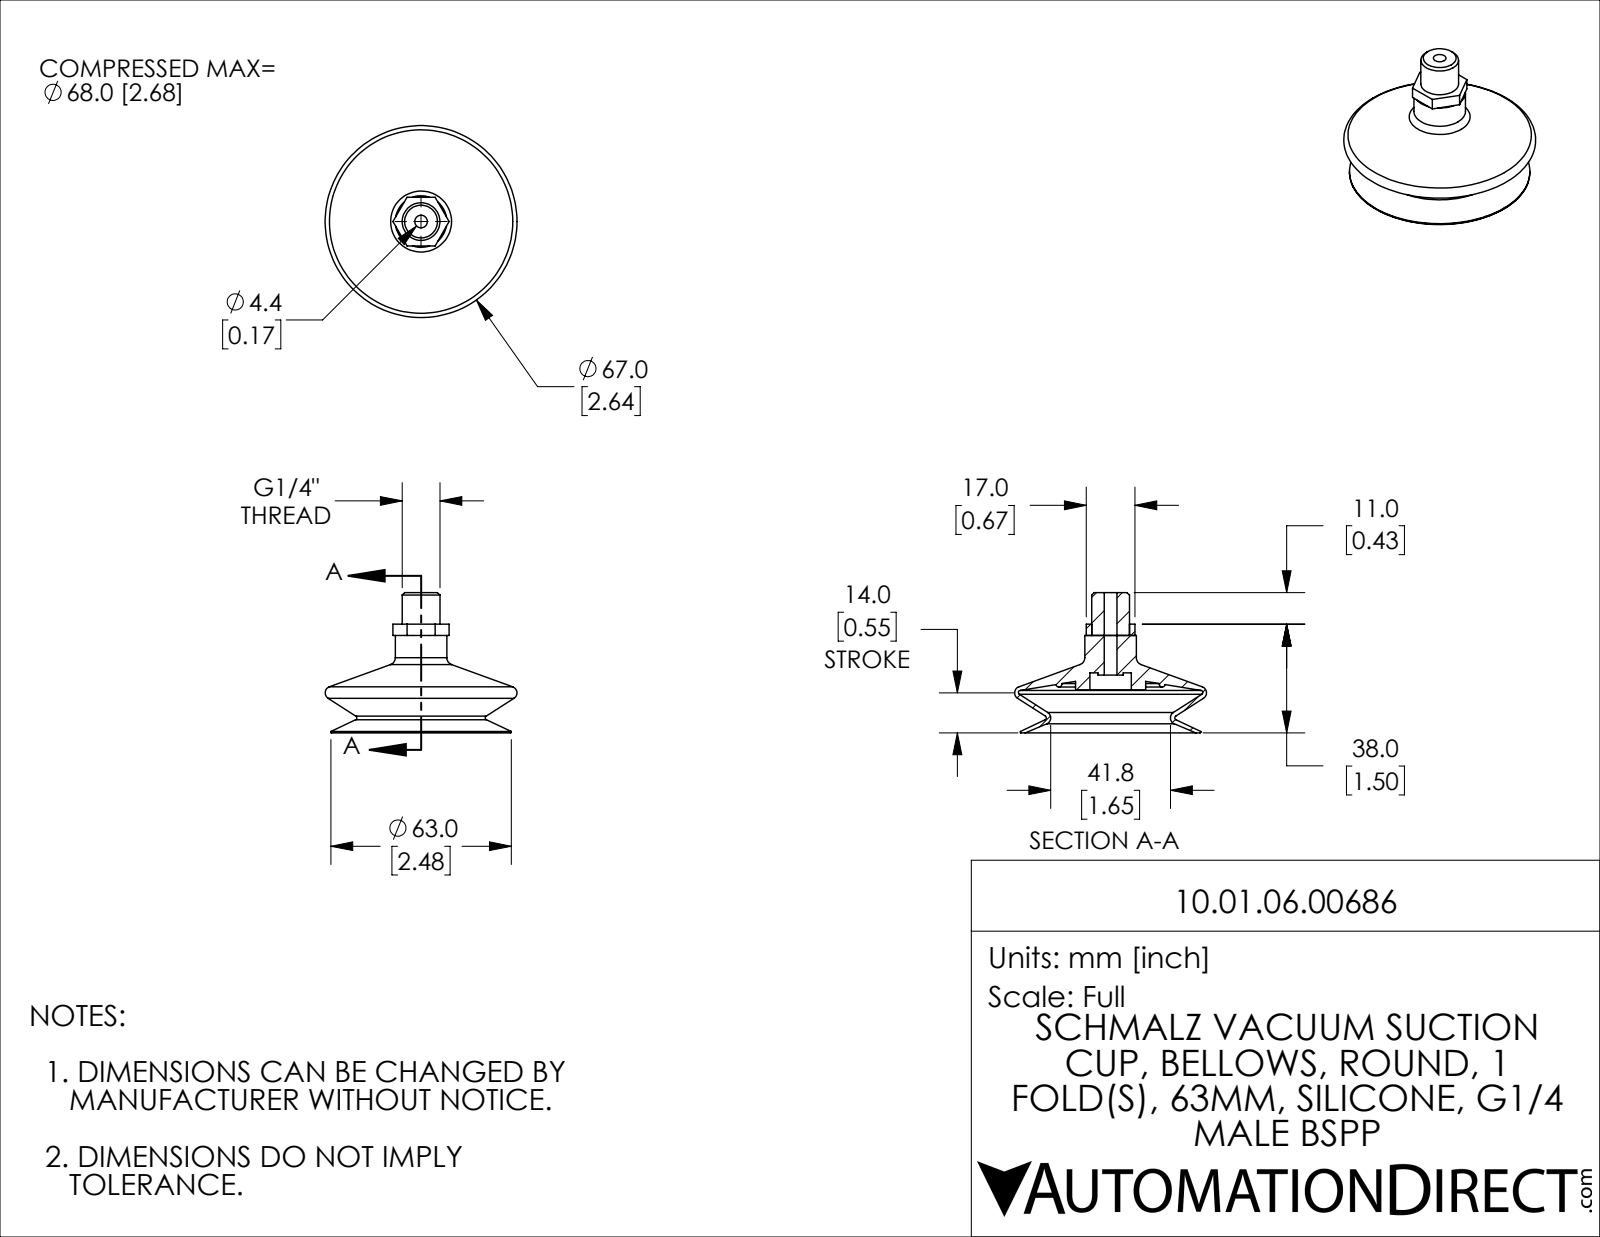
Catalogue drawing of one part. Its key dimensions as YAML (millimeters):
part_name: "10.01.06.00686"
step_written_by: "SolidWorks 2021 (CONFIG_CONTROL_DESIGN)"
units: millimeters
bodies: {solids: 3, faces: 71, planar: 15, cylindrical: 16, other: 40}
overall_size: [67, 67, 49]
volume: 22958
surface_area: 19241
round_holes:
  - {diameter: 4.4, count: 1}
  - {diameter: 13.16, count: 1}
  - {diameter: 14.5, count: 1}
round_bosses_or_shafts:
  - {diameter: 63, count: 1}
  - {diameter: 24.5, count: 1}
  - {diameter: 8.8, count: 1}
face_to_face_distances: [15, 34, 19, 17, 38, 23, 4, 21, 6, 13]
